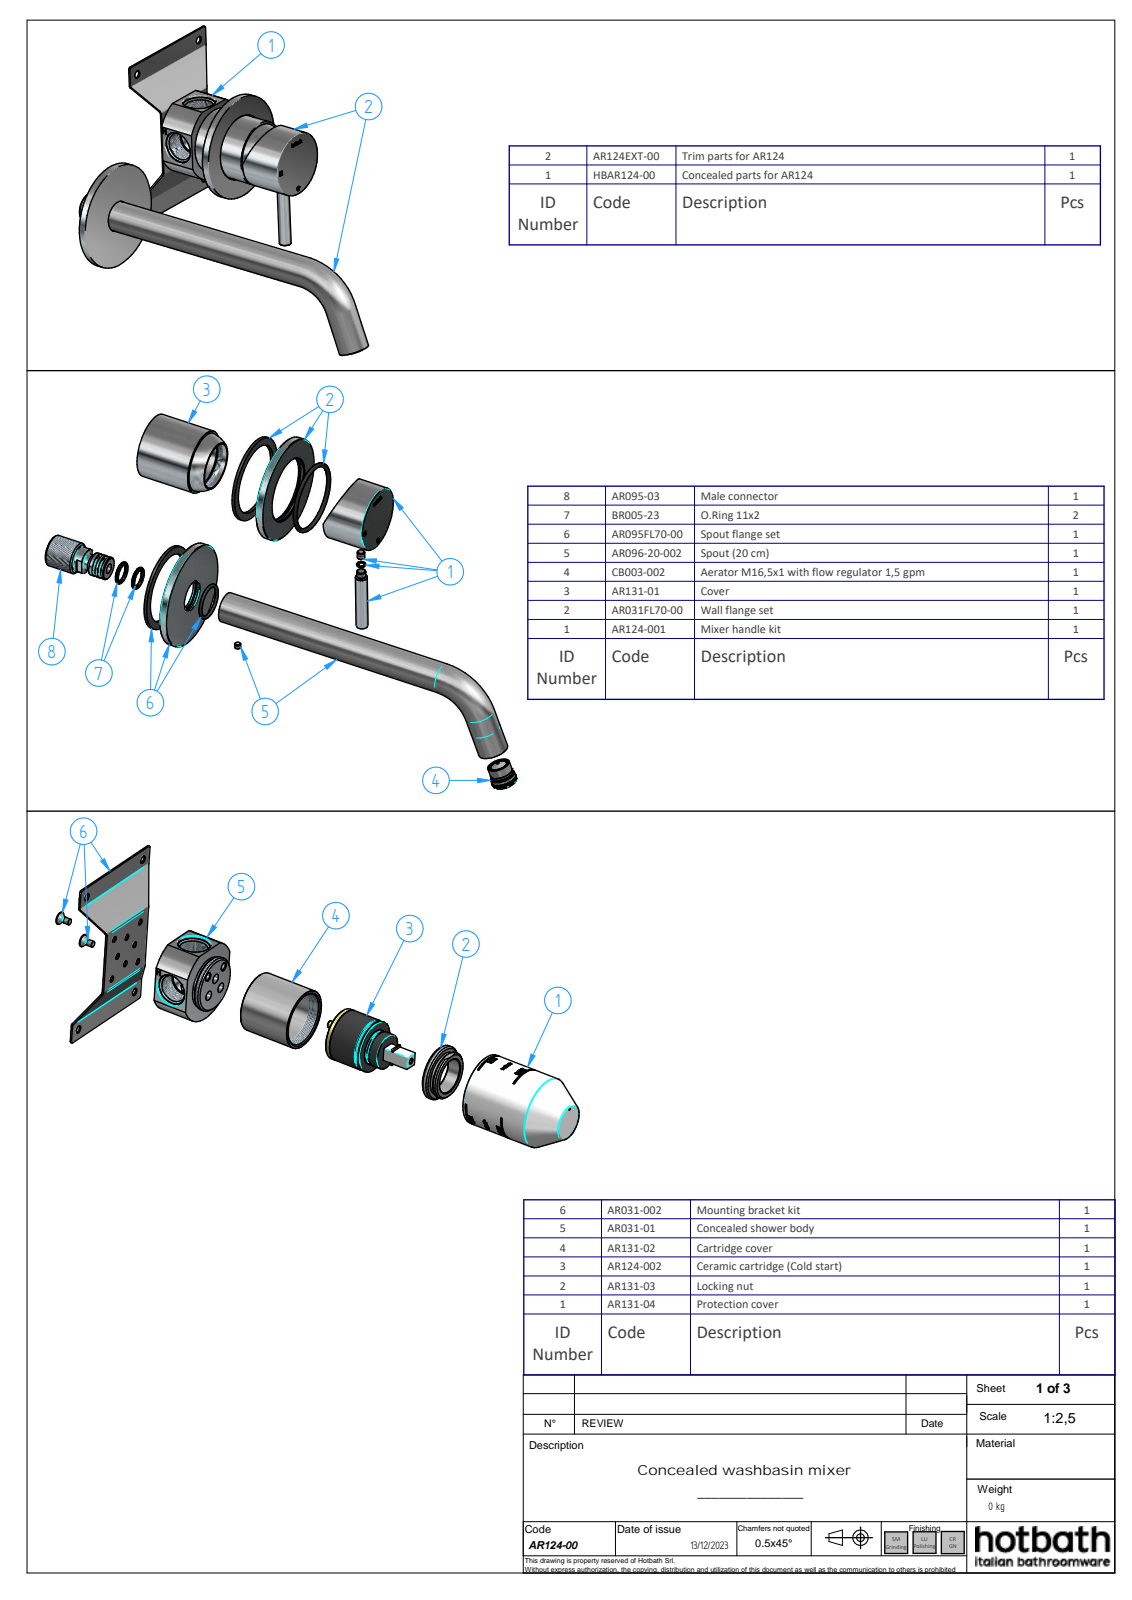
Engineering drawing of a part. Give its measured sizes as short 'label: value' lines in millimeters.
name: AR124EXT-00; AR124-001; AR031-08; AR124-01 (+8 more)
written by: Solid Edge (AUTOMOTIVE_DESIGN)
unit: mm
bodies: 20 solids, 368 faces (193 planar, 84 cylindrical, 91 other)
size: 229.69 × 199.9 × 95.5
volume: 104 125 mm³; area: 78 006 mm²
holes: 2× ⌀15, 2× ⌀47, 1× ⌀3.24, 1× ⌀4.2, 1× ⌀5.1, 1× ⌀6.5, 1× ⌀8.2, 1× ⌀10, 1× ⌀11.03, 1× ⌀12.2, 1× ⌀14.58, 1× ⌀15.42
bosses: 3× ⌀20, 1× ⌀70, 1× ⌀69.8, 1× ⌀57, 1× ⌀43, 1× ⌀42.8, 1× ⌀20.95, 1× ⌀18
rounds: 2× R0.24, 2× R0.39, 2× R0.44, 2× R0.69, 1× R0.62, 1× R0.62, 1× R0.63, 1× R0.63
face distances: 5, 1.2, 0.5, 4.5, 2, 1.7, 3.3, 52.03, 51.53, 50.33
hole spacings: 130, 133.47
